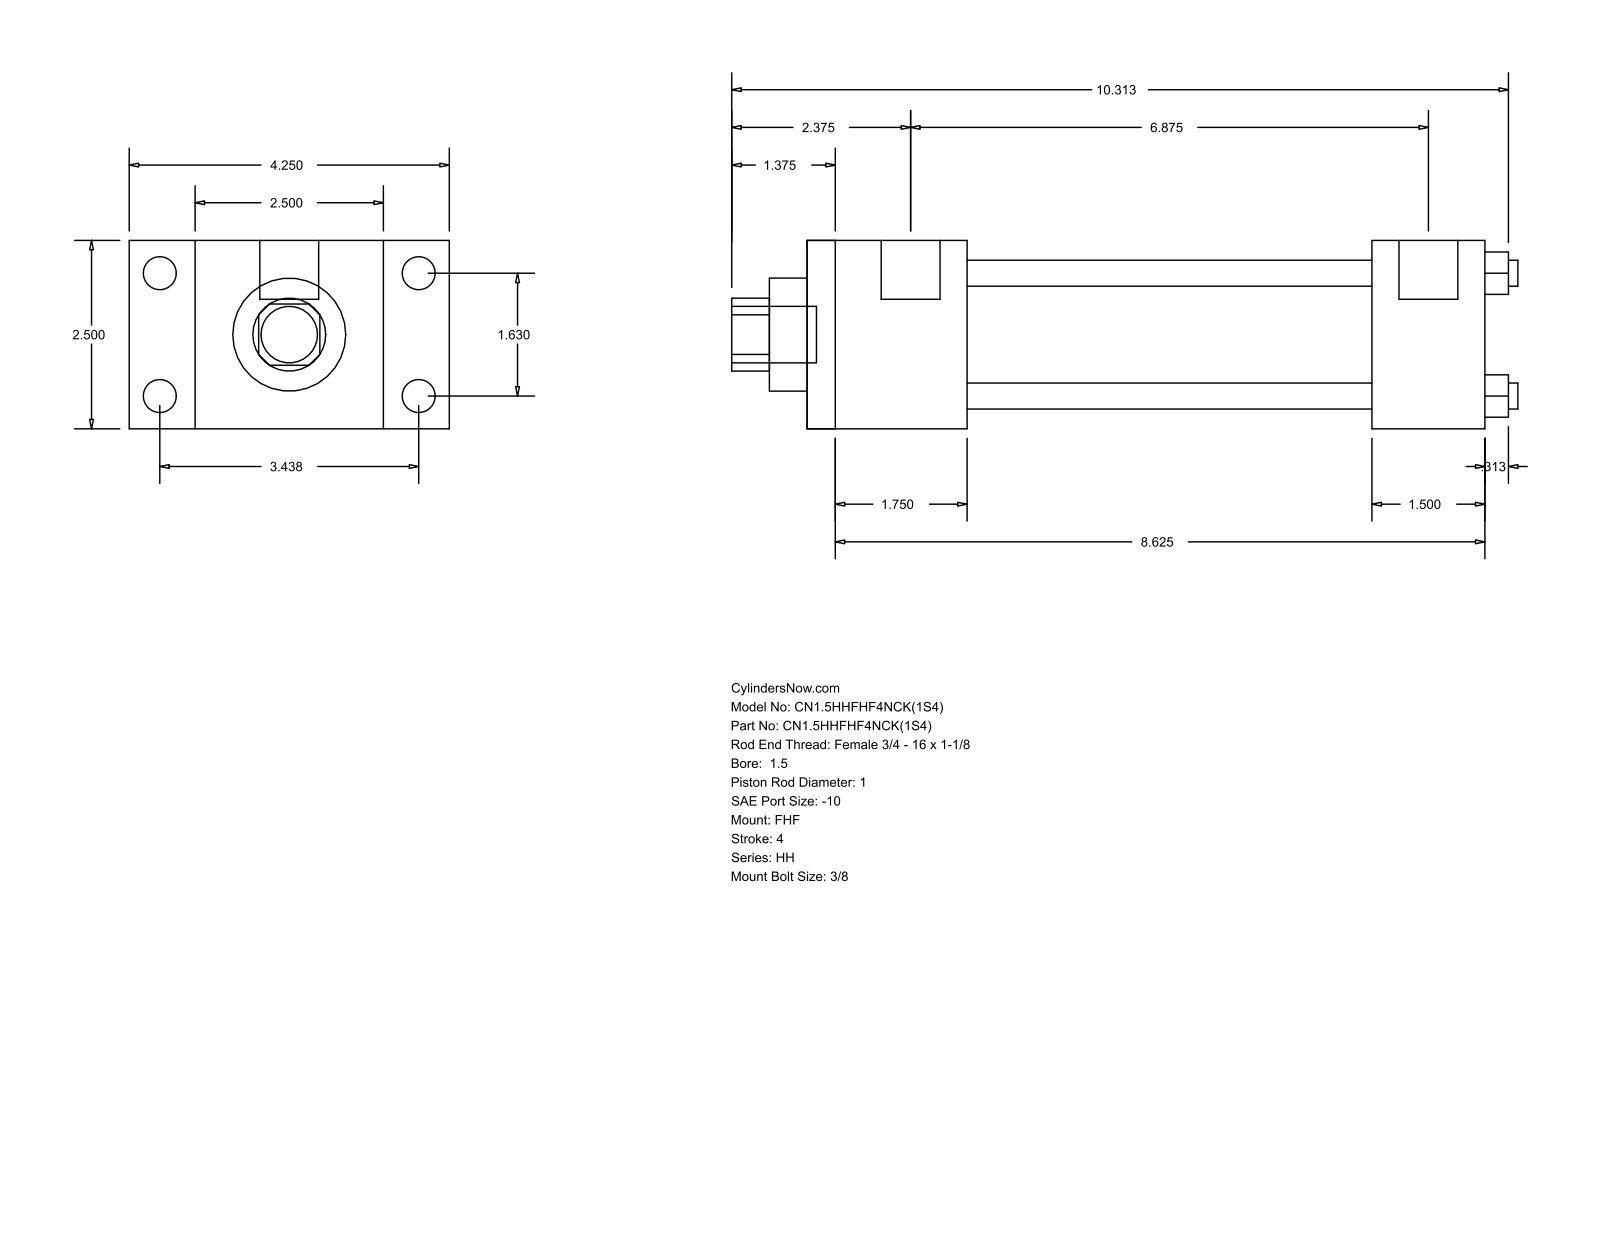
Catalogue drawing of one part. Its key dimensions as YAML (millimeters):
part_name: "HH_FHF__0150_1"
step_written_by: "GSSL Pune (CONFIG_CONTROL_DESIGN)"
units: millimeters
bodies: {solids: 0, faces: 88, planar: 60, cylindrical: 28, other: 0}
overall_size: [265.11, 107.95, 63.5]
round_holes:
  - {diameter: 8.76, count: 4}
  - {diameter: 25.4, count: 1}
  - {diameter: 38.1, count: 1}
  - {diameter: 44.45, count: 1}
round_bosses_or_shafts:
  - {diameter: 11.13, count: 4}
  - {diameter: 5.56, count: 4}
  - {diameter: 19.84, count: 2}
  - {diameter: 19.05, count: 1}
partial_cylinders:
  - {radius: 12.29, count: 1}
face_to_face_distances: [63.5, 22.23, 85.73, 53.98, 107.96, 228.6, 174.62, 190.5, 136.52, 38.1]
hole_center_spacings: [29.27, 41.4, 58.55]
